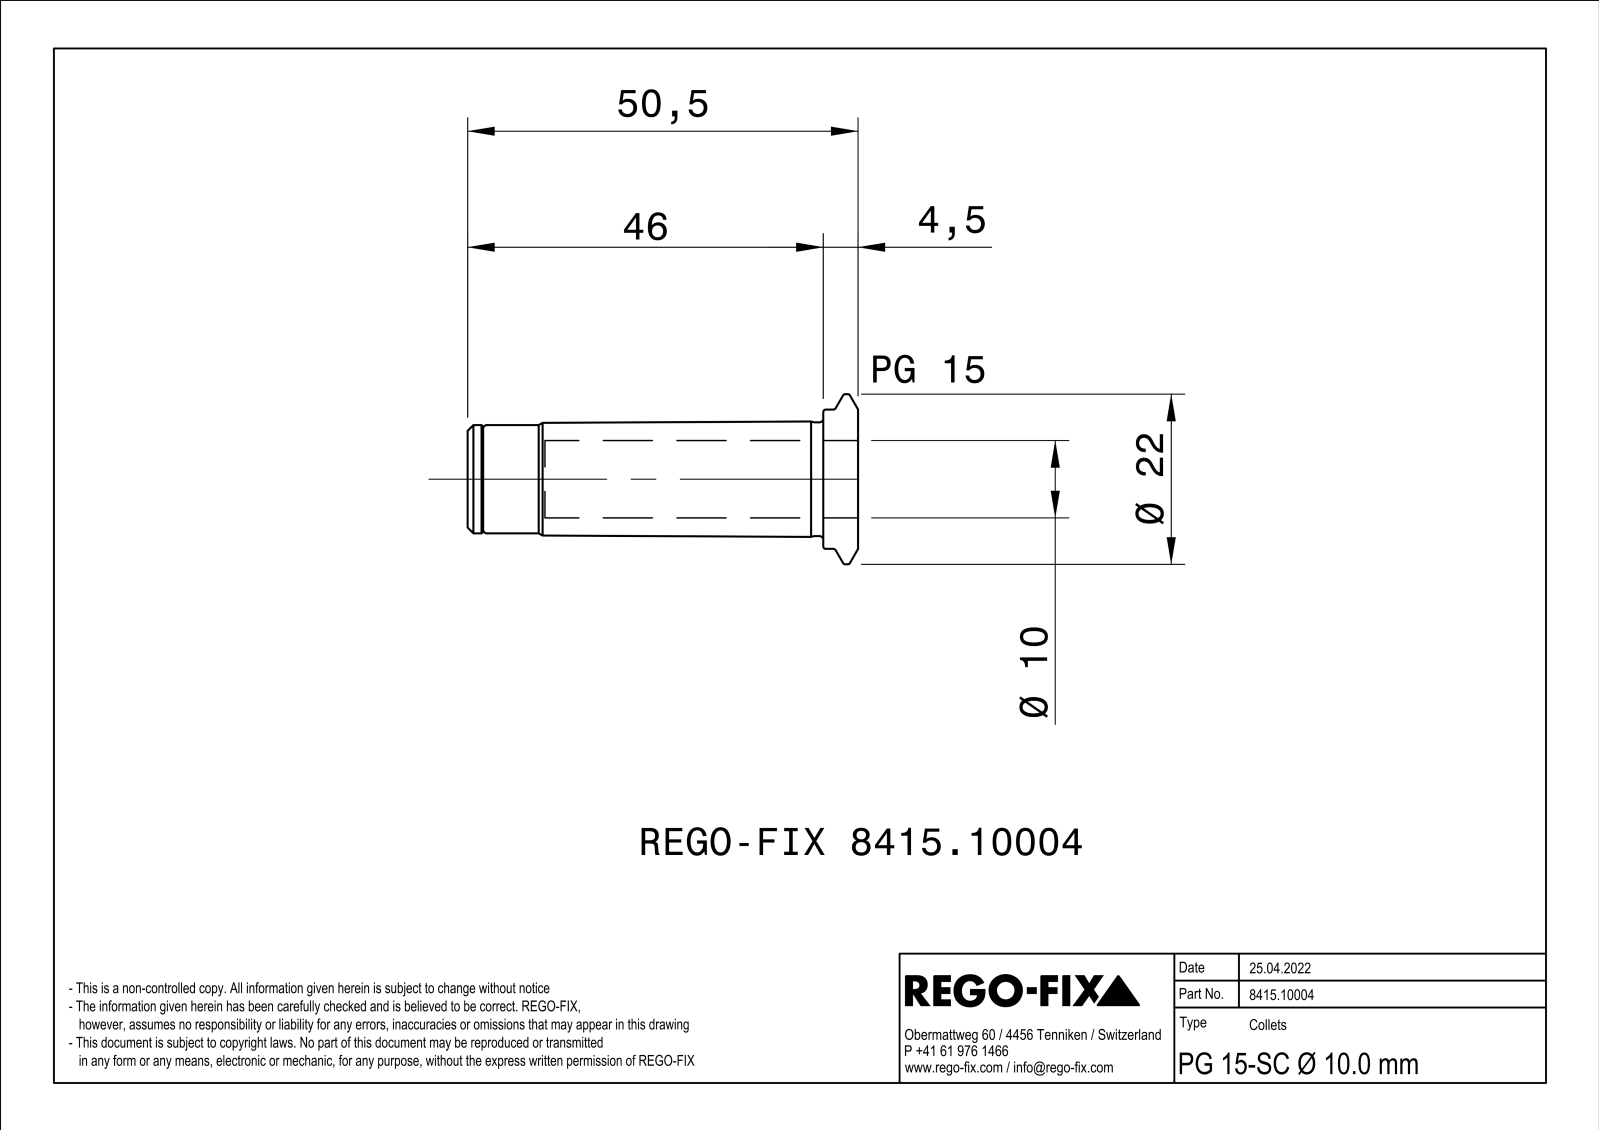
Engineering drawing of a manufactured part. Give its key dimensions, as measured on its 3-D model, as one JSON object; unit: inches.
{"part_name": "NOCUT", "step_written_by": "SIEMENS PLM Software Solid Edge ST10 (AUTOMOTIVE_DESIGN)", "units": "inches", "bodies": {"solids": 2, "faces": 107, "planar": 39, "cylindrical": 30, "other": 38}, "overall_size": [1.988, 0.866, 0.866], "volume_in3": 0.32, "surface_area_in2": 8.844, "round_holes": [[0.059, 2], [0.272, 1], [0.283, 1], [0.323, 1], [0.394, 1], [0.43, 1], [0.48, 1]], "round_bosses_or_shafts": [[0.866, 1], [0.709, 1], [0.579, 1], [0.551, 1]], "partial_cylinders_radius": [[0.006, 4], [0.205, 1], [0.236, 1]], "face_to_face_distances": [1.909, 0.079, 1.988, 0.315, 0.118, 0.183, 0.171, 0.177, 1.732, 1.811]}
